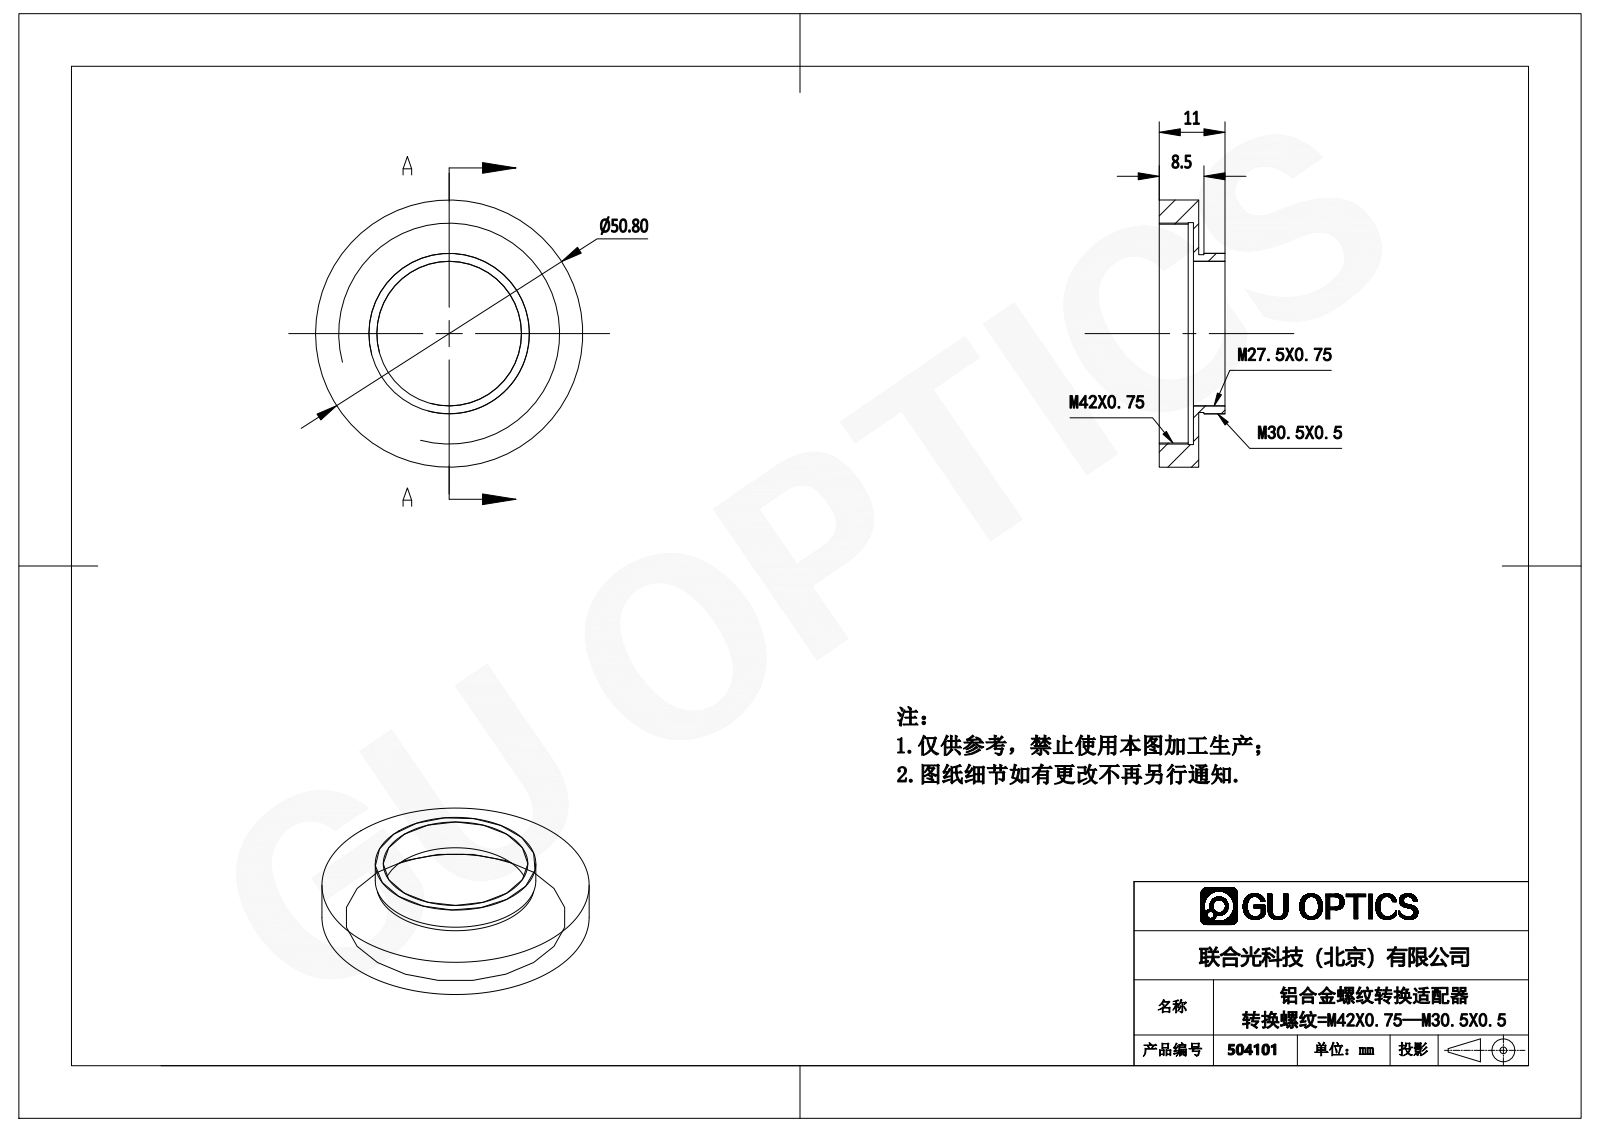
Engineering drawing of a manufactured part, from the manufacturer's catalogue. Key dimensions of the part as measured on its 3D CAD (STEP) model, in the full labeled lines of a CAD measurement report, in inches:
Part name (STEP PRODUCT): 504101
STEP written by: SolidWorks 2016 (AUTOMOTIVE_DESIGN)
Units: inches
Bodies: 1 solid, 18 faces (6 planar, 12 cylindrical, 0 other)
Overall size (bounding box): 2 × 2 × 0.492
Volume: 0.391 in³ · Surface area: 9.362 in²
Round holes (diameter × count): ⌀1.082 ×1, ⌀1.638 ×1, ⌀1.661 ×1
Round bosses / shafts (diameter × count): ⌀2 ×1, ⌀1.202 ×1, ⌀1.181 ×1
Main face-to-face distances: 0.039, 0.256, 0.295, 0.492, 0.236, 0.197, 0.079, 0.217, 0.276, 0.335
